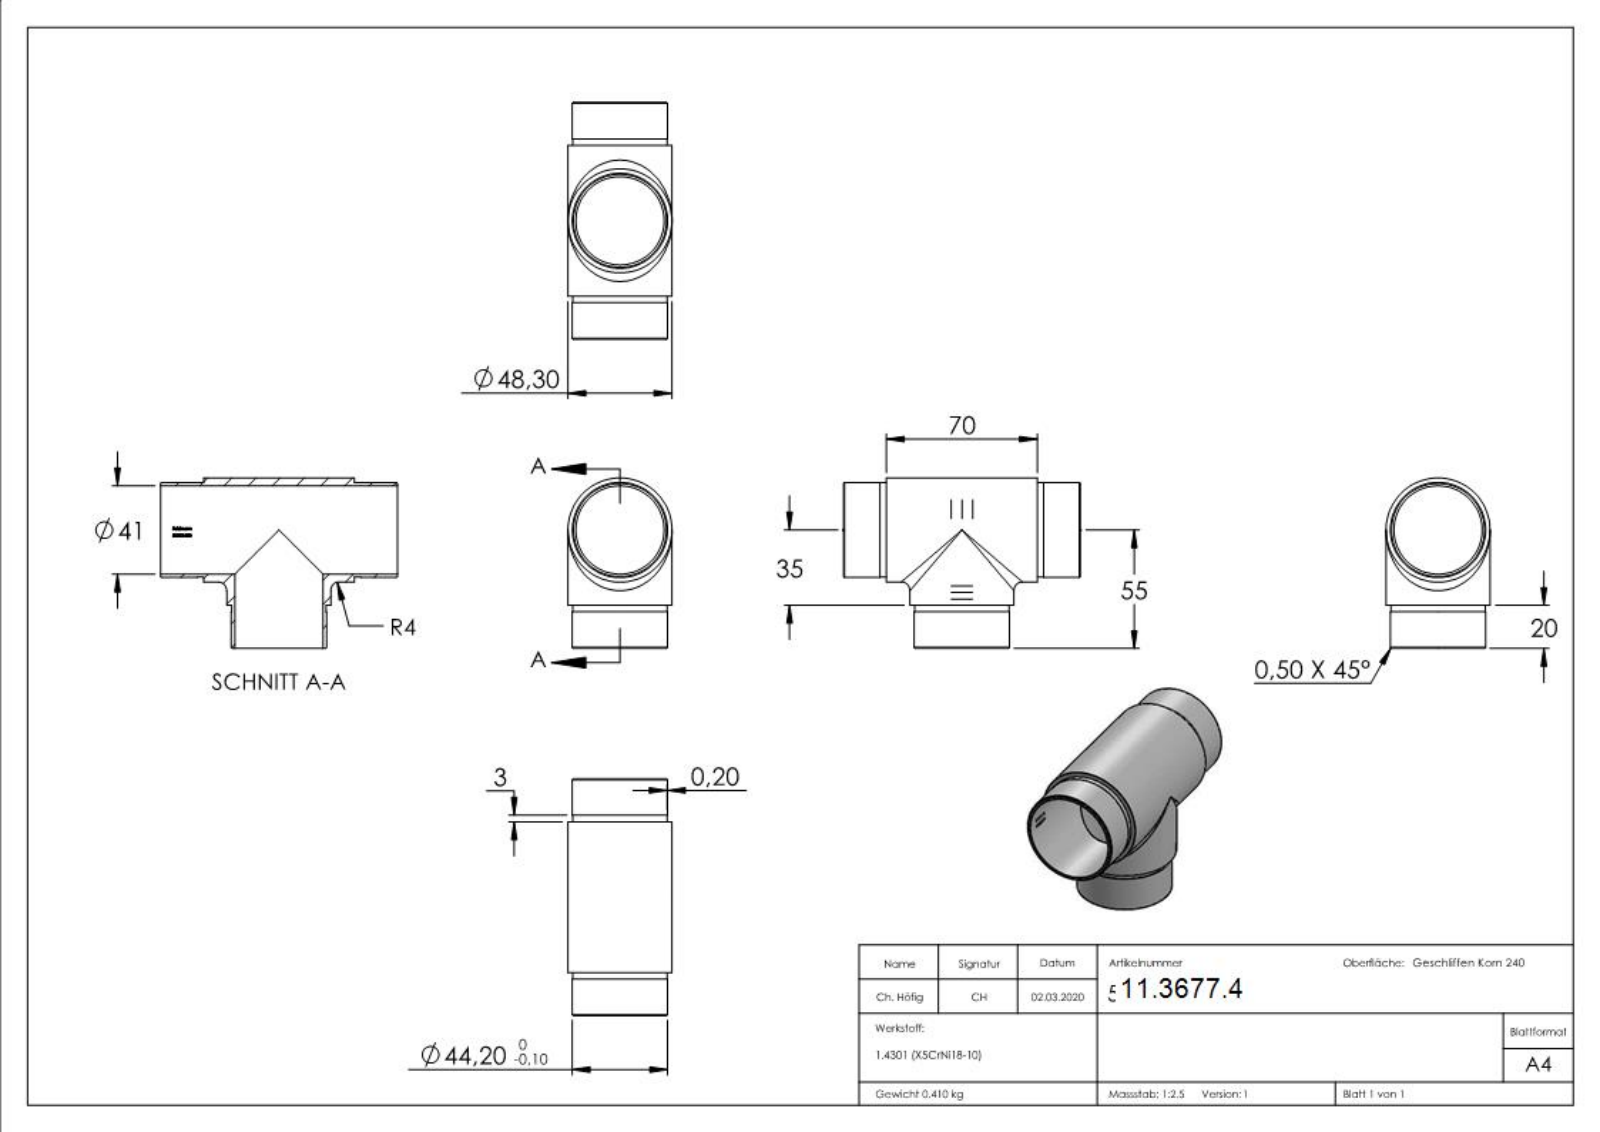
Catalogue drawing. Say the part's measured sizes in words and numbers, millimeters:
The part is named "56212-320". Its 3-D file was written by "SolidWorks 2015 (CONFIG_CONTROL_DESIGN)". It is 1 solid with 246 faces: 103 planar, 32 cylindrical and 111 other. Overall it measures 110 by 79.15 by 48.3 millimeters. Its volume is 51 928 cubic millimeters and its surface area 38 972 square millimeters. Round holes: 2 of diameter 41. Round bosses or shafts: 2 of diameter 48.3, 2 of diameter 44.2, 2 of diameter 43.8. Partial cylindrical surfaces (rounded edges, fillets, slot ends): 1 of radius 20.6. The main face-to-face distances are 20, 70, 90, 110, 17, 3, 93, 73, 76, 3.53.
